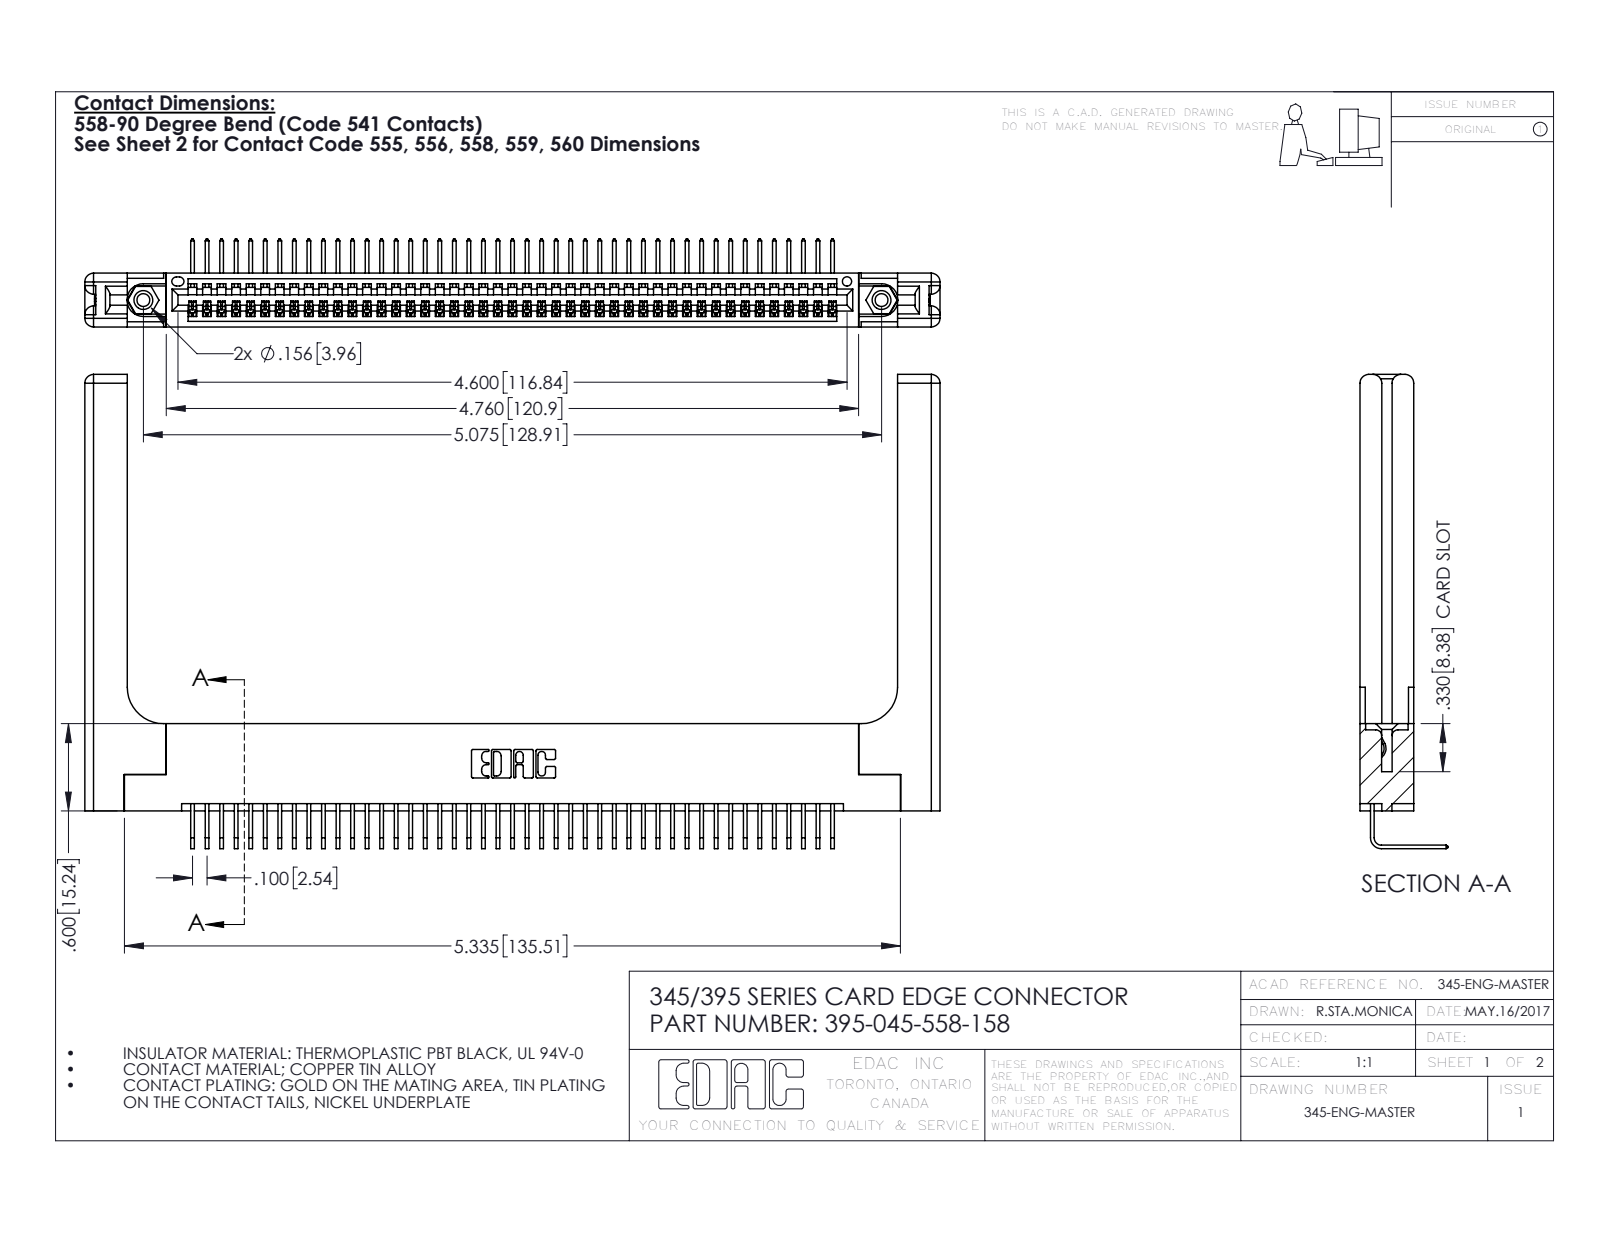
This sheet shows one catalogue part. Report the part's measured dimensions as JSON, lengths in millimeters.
{"part_name": "345-292-001_558 Tail - 2; 395-045-558-158; 345 Part_Flush Mounting Lugs - 0.156 Dia-TH; 345-220-058_345-220-058 (+1 more)", "step_written_by": "SolidWorks 2016 (CONFIG_CONTROL_DESIGN)", "units": "millimeters", "bodies": {"solids": 50, "faces": 3082, "planar": 2118, "cylindrical": 904, "other": 60}, "overall_size": [149.3, 82.8, 15.4], "volume_mm3": 22860, "surface_area_mm2": 25310, "round_holes": [[2.3, 2], [3.2, 2], [4, 2], [1.6, 1]], "round_bosses_or_shafts": [[3.9, 2]], "partial_cylinders_radius": [[0.2, 90], [0.3, 22], [1.5, 16], [0.2, 6], [0.8, 6], [0.7, 3], [0.8, 2], [0.8, 2]], "face_to_face_distances": [1.8, 9.4, 7.6, 5.1, 2.5, 6.9, 0.6, 5.7, 3.8, 3.8], "hole_center_spacings": [6.9, 122.9, 128.9]}
